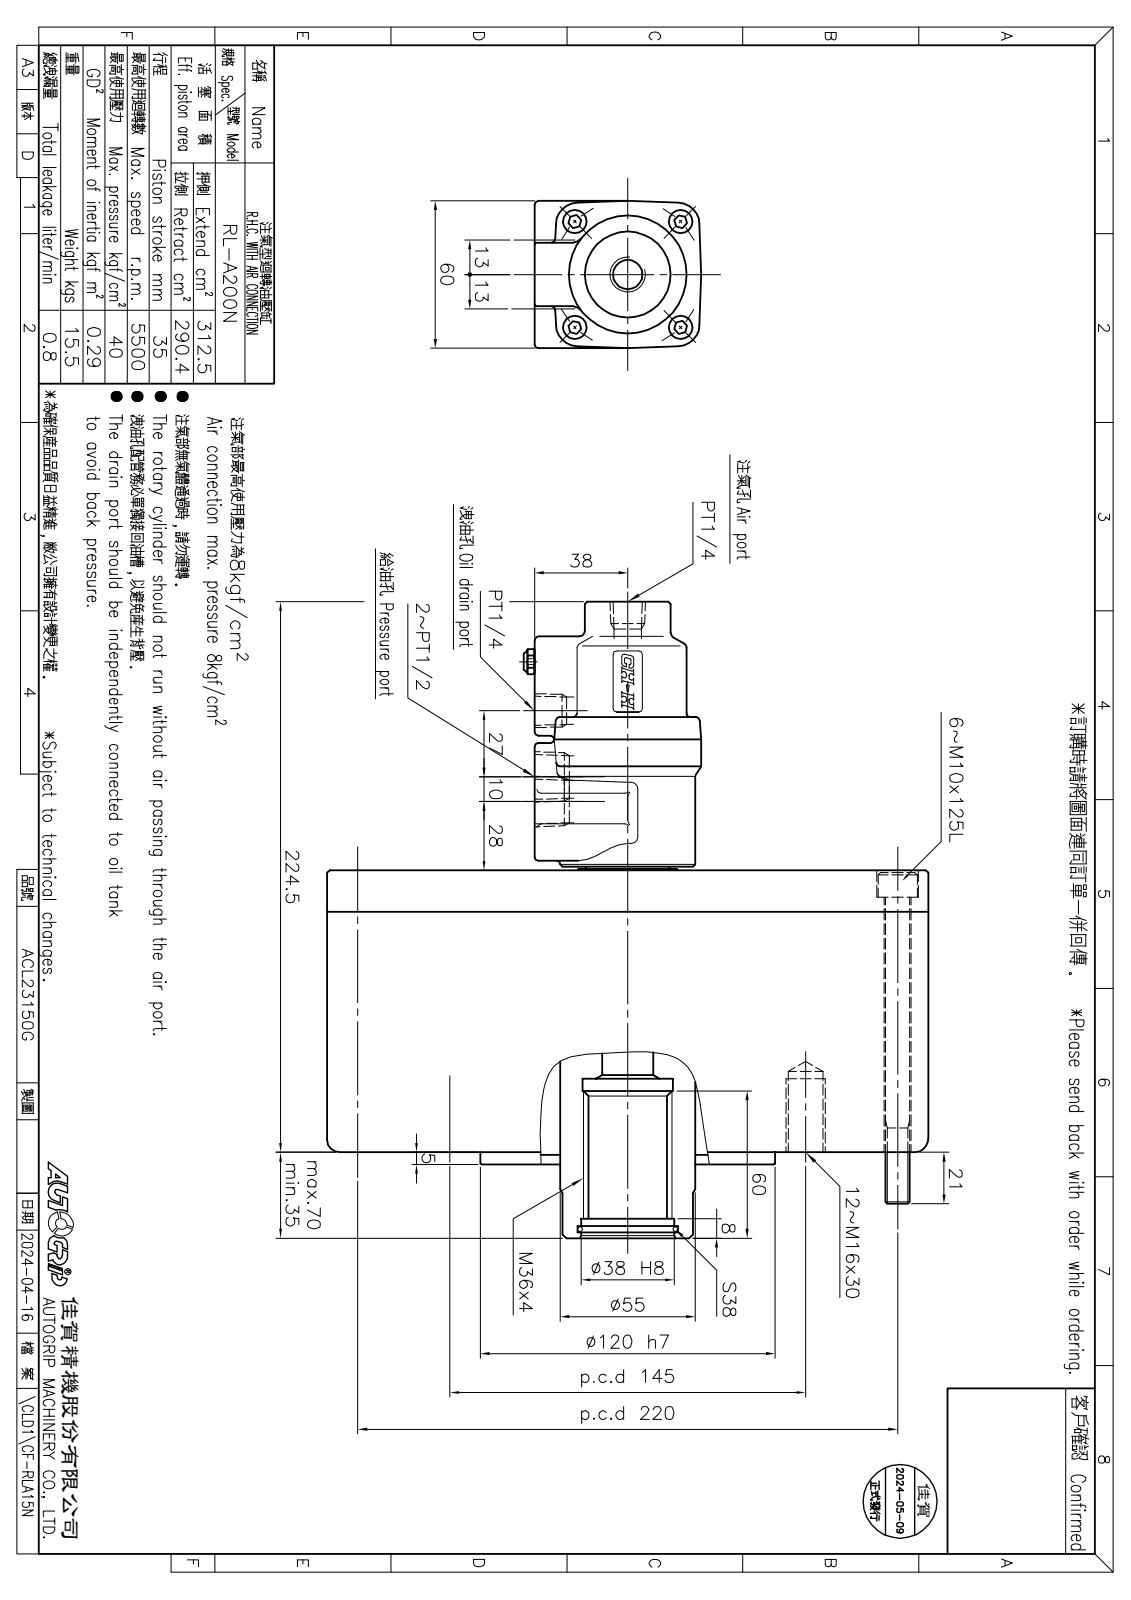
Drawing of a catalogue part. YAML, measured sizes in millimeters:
part_name: "RL-200活塞; RK-200缸體; RL-A100N消音器; RL-A200N組合件"
step_written_by: "SolidWorks 2010 (CONFIG_CONTROL_DESIGN)"
units: millimeters
bodies: {solids: 6, faces: 458, planar: 97, cylindrical: 178, other: 183}
overall_size: [259.5, 245, 245]
volume: 4564000
surface_area: 509125
round_holes:
  - {diameter: 14, count: 12}
  - {diameter: 16, count: 12}
  - {diameter: 11, count: 6}
  - {diameter: 12, count: 6}
  - {diameter: 17, count: 6}
  - {diameter: 11.2, count: 2}
  - {diameter: 14.7, count: 2}
  - {diameter: 2.6, count: 1}
  - {diameter: 4.1, count: 1}
  - {diameter: 5, count: 1}
  - {diameter: 30, count: 1}
  - {diameter: 36, count: 1}
round_bosses_or_shafts:
  - {diameter: 245, count: 1}
  - {diameter: 200, count: 1}
  - {diameter: 120, count: 1}
  - {diameter: 55, count: 1}
  - {diameter: 53, count: 1}
  - {diameter: 48, count: 1}
  - {diameter: 35, count: 1}
  - {diameter: 3.8, count: 1}
partial_cylinders:
  - {radius: 1.5, count: 24}
  - {radius: 6, count: 4}
  - {radius: 9, count: 4}
  - {radius: 2, count: 3}
  - {radius: 5, count: 2}
  - {radius: 15, count: 2}
face_to_face_distances: [75, 40, 25, 35, 17, 58, 8, 50, 90, 115]
hole_center_spacings: [72.5, 77.96, 110, 140.06, 37.53, 44.15, 72.51, 102.53]
